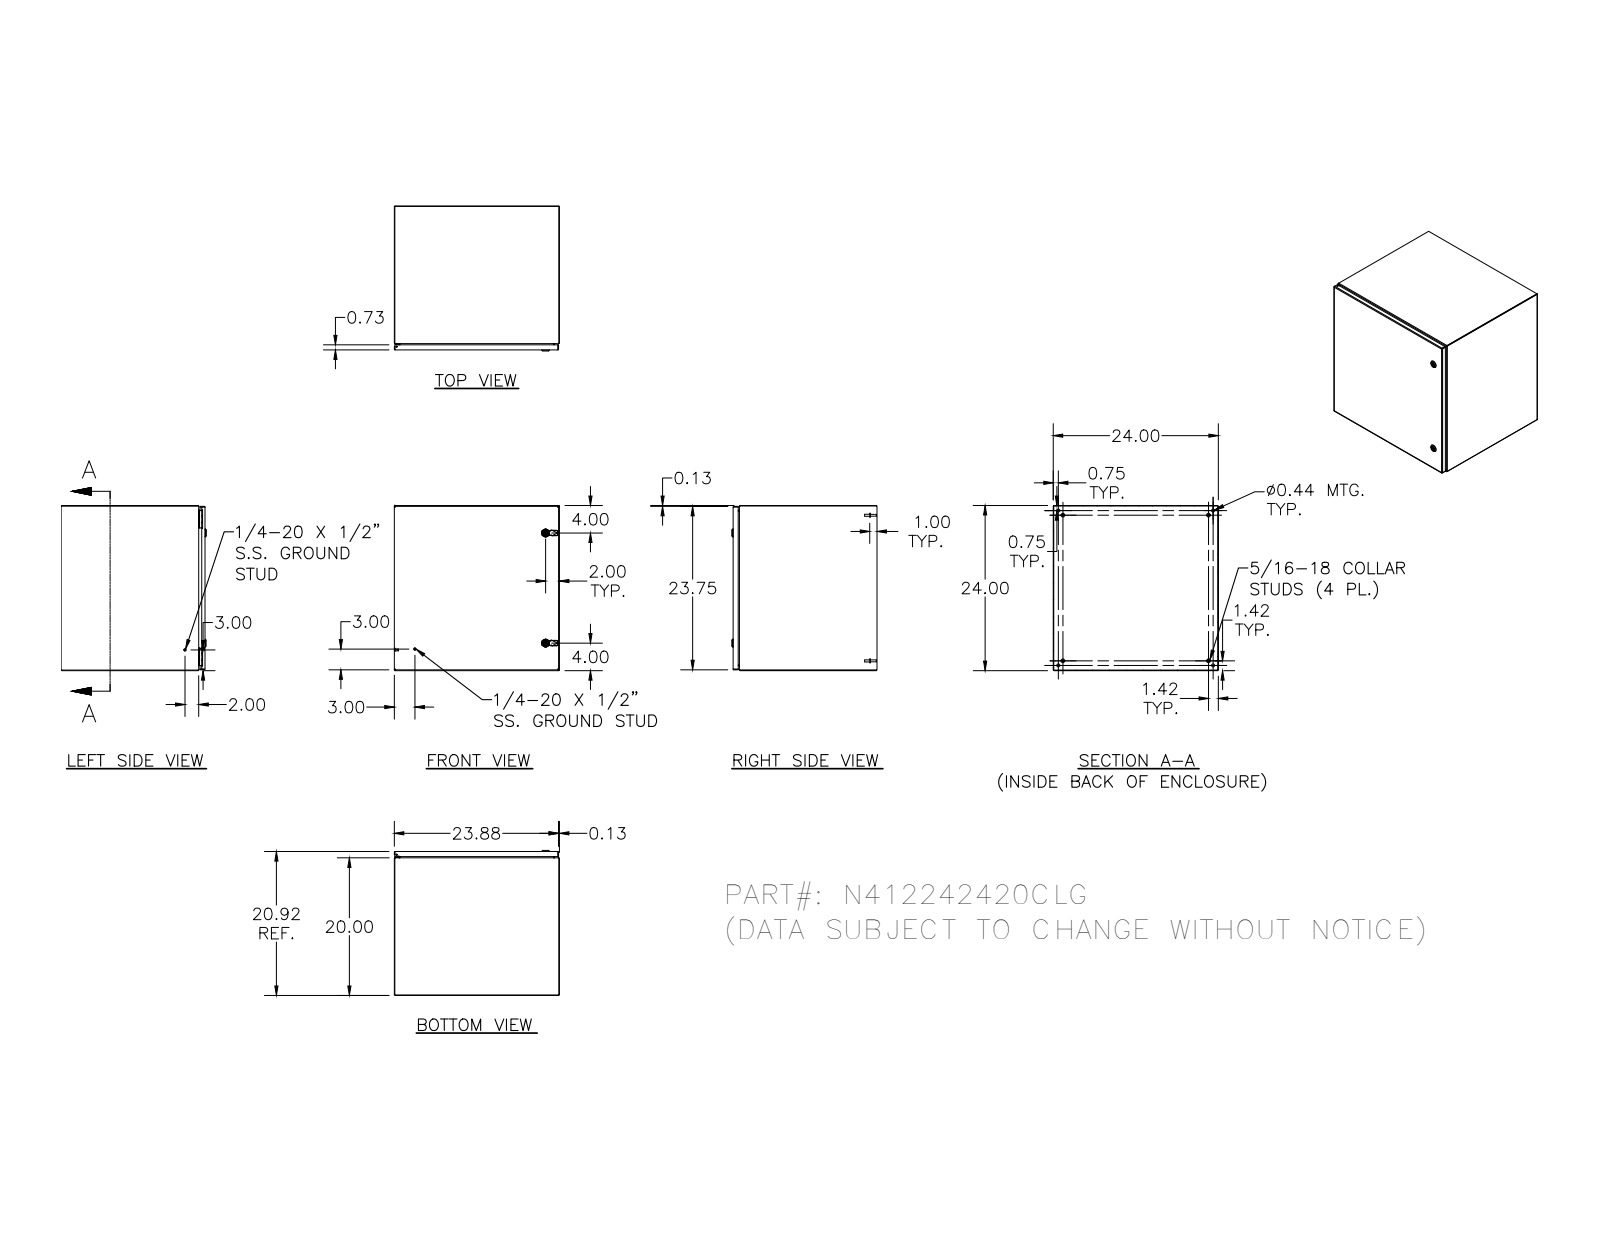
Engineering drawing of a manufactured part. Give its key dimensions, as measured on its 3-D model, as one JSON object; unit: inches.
{"part_name": "N412242420CLG", "step_written_by": "SolidWorks 2018 (AUTOMOTIVE_DESIGN)", "units": "inches", "bodies": {"solids": 42, "faces": 1786, "planar": 702, "cylindrical": 660, "other": 424}, "overall_size": [24, 24, 21.075], "volume_in3": 241.4, "surface_area_in2": 6556, "round_holes": [[0.188, 5], [0.093, 4], [0.152, 4], [0.167, 4], [0.172, 4], [0.438, 4], [0.156, 2], [0.197, 2], [0.315, 2], [0.394, 2], [0.402, 2], [0.634, 2]], "round_bosses_or_shafts": [[0.25, 10], [0.563, 4], [0.36, 4], [0.32, 4], [0.3, 4], [0.275, 4], [0.256, 4], [0.164, 4]], "partial_cylinders_radius": [[0.012, 54], [0.031, 28], [0.05, 26], [0.02, 23], [0.016, 18], [0.105, 18], [0.125, 16], [0.032, 8]], "face_to_face_distances": [0.074, 23.926, 20.843, 23.852, 24, 20.769, 20.917, 19.926, 0.917, 0.739], "hole_center_spacings": [20.004, 22.5, 0.5, 0.656, 0.66, 0.984, 1.615, 1.618]}
